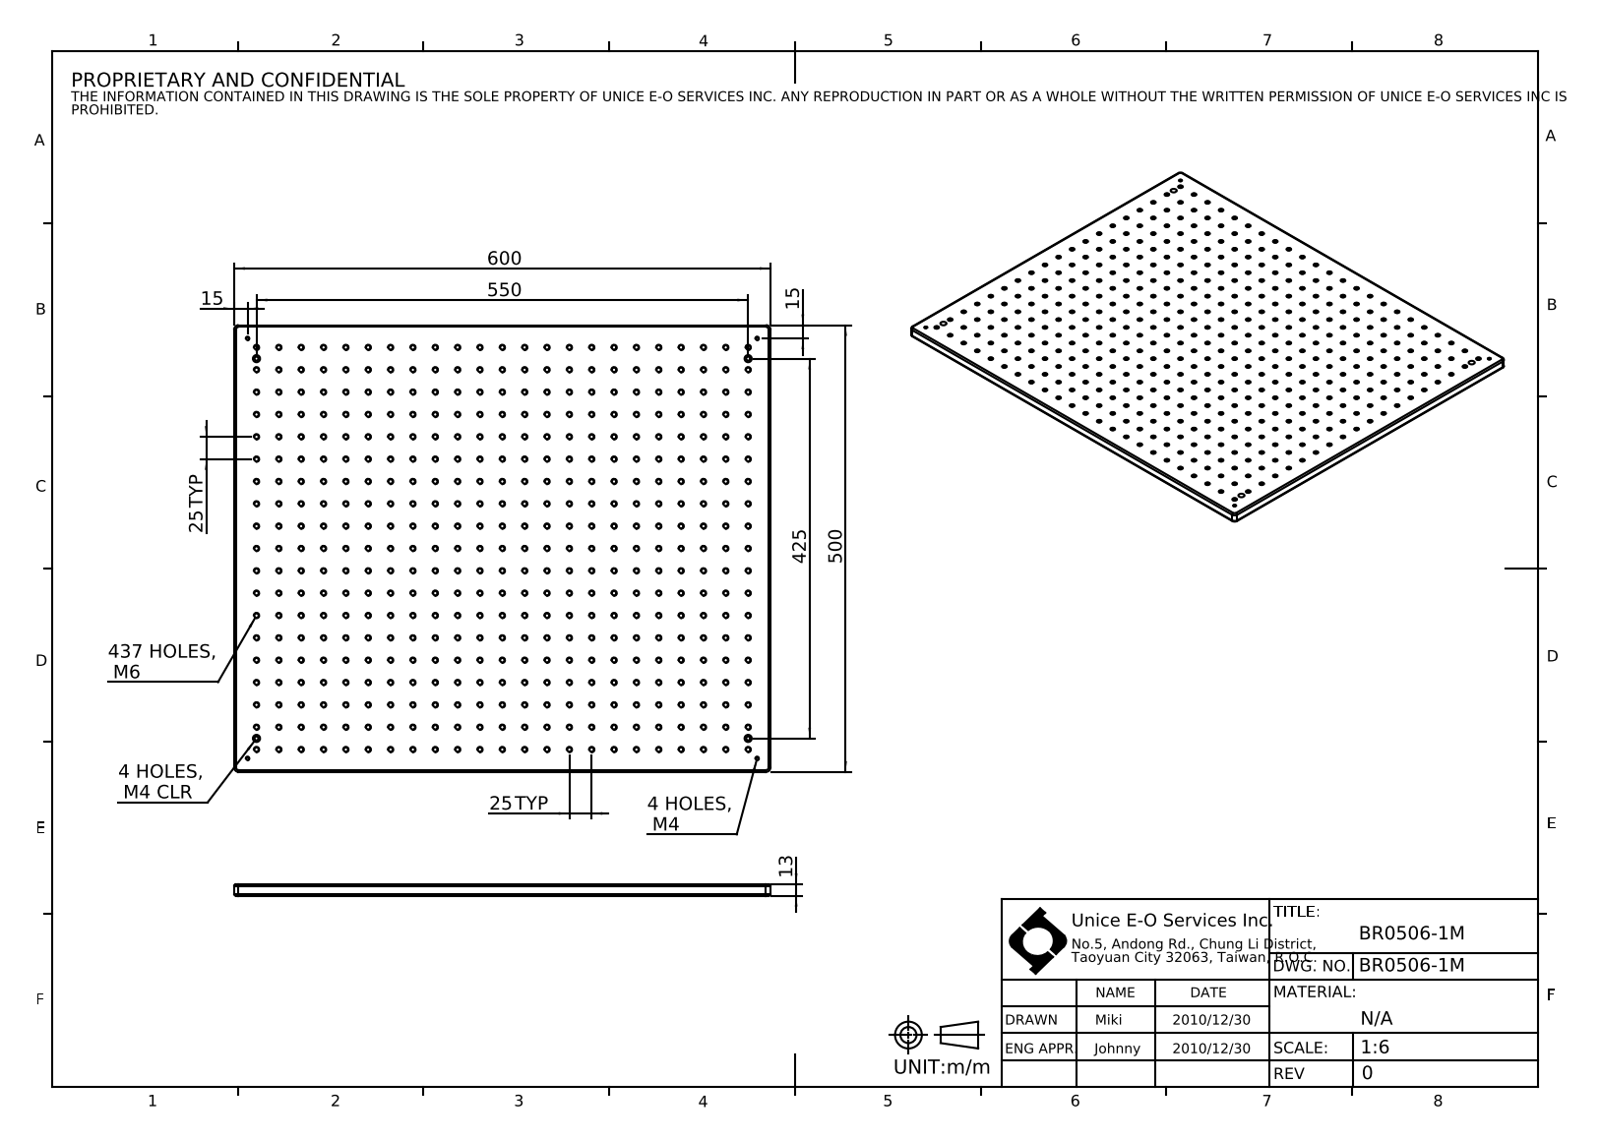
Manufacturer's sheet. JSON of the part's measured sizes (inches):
{"part_name": "BR0506-1M", "step_written_by": "SolidWorks 2016 (CONFIG_CONTROL_DESIGN)", "units": "inches", "bodies": {"solids": 1, "faces": 928, "planar": 10, "cylindrical": 910, "other": 8}, "overall_size": [23.622, 19.685, 0.512], "volume_in3": 230.8, "surface_area_in2": 1082, "round_holes": [[0.197, 437], [0.13, 4], [0.177, 4], [0.315, 4]], "partial_cylinders_radius": [[0.079, 8], [0.197, 4]], "face_to_face_distances": [0.512, 19.685, 23.622, 0.276, 0.236], "hole_center_spacings": [0.984, 1.969, 2.953, 3.937, 4.921, 5.906, 6.89, 7.874]}
